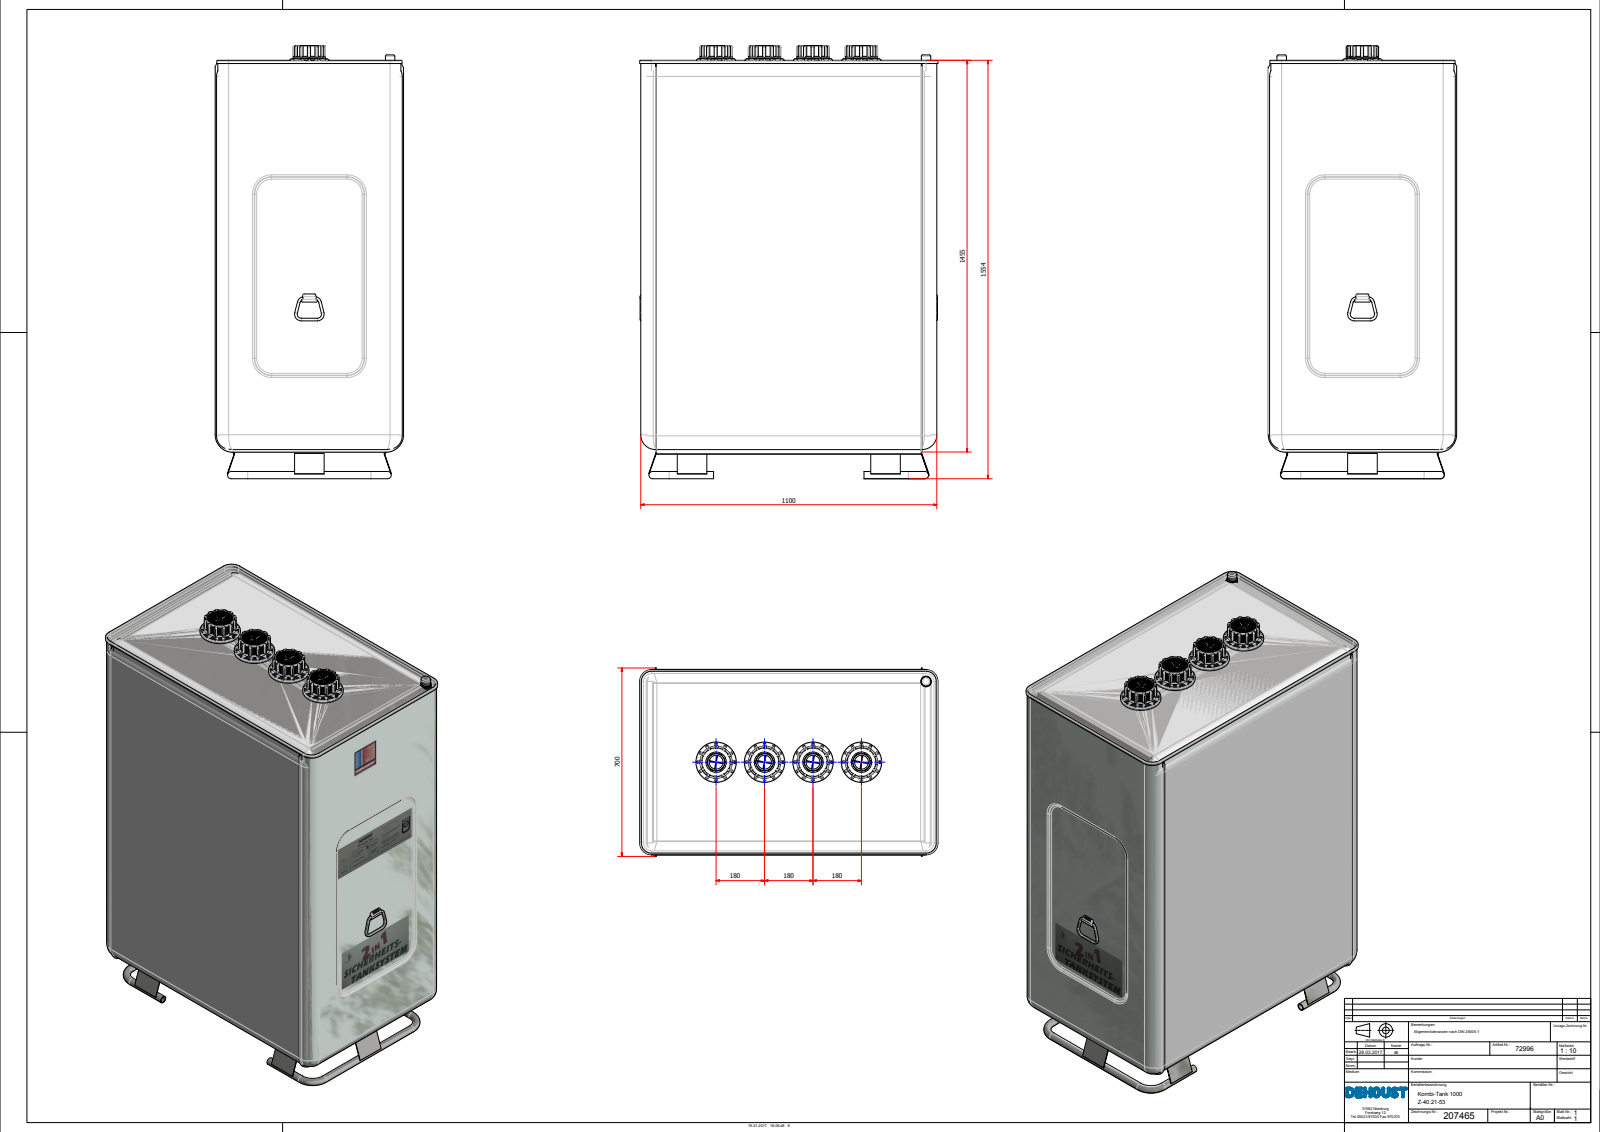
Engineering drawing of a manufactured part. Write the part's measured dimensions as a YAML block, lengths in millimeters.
part_name: "Kombi-Tank 1000; Fuß_Kombi-Tank; Rahmen; Kantung Fußrahmen (+8 more)"
step_written_by: "Autodesk Inventor 2017 (AUTOMOTIVE_DESIGN)"
units: millimeters
bodies: {solids: 42, faces: 2281, planar: 827, cylindrical: 853, other: 601}
overall_size: [1610.16, 1108, 700]
volume: 28800000
surface_area: 27180000
round_holes:
  - {diameter: 22.5, count: 6}
  - {diameter: 51.5, count: 4}
  - {diameter: 56.66, count: 4}
  - {diameter: 58, count: 4}
  - {diameter: 61, count: 4}
  - {diameter: 68, count: 4}
  - {diameter: 73, count: 4}
  - {diameter: 76, count: 4}
  - {diameter: 90, count: 4}
  - {diameter: 93, count: 4}
  - {diameter: 99.5, count: 4}
  - {diameter: 100, count: 4}
round_bosses_or_shafts:
  - {diameter: 26.9, count: 6}
  - {diameter: 10, count: 6}
  - {diameter: 150, count: 4}
  - {diameter: 120, count: 4}
  - {diameter: 98, count: 4}
  - {diameter: 86.2, count: 4}
  - {diameter: 86, count: 4}
  - {diameter: 85, count: 4}
partial_cylinders:
  - {radius: 2, count: 194}
  - {radius: 1, count: 146}
  - {radius: 10, count: 28}
  - {radius: 1.5, count: 24}
  - {radius: 3, count: 12}
  - {radius: 8, count: 12}
  - {radius: 47, count: 12}
  - {radius: 1.25, count: 8}
face_to_face_distances: [3, 1, 684, 2, 679, 6, 5, 681, 682, 685]
hole_center_spacings: [581.04, 180, 360, 385.28, 517.13, 540, 671.72, 836.53]
